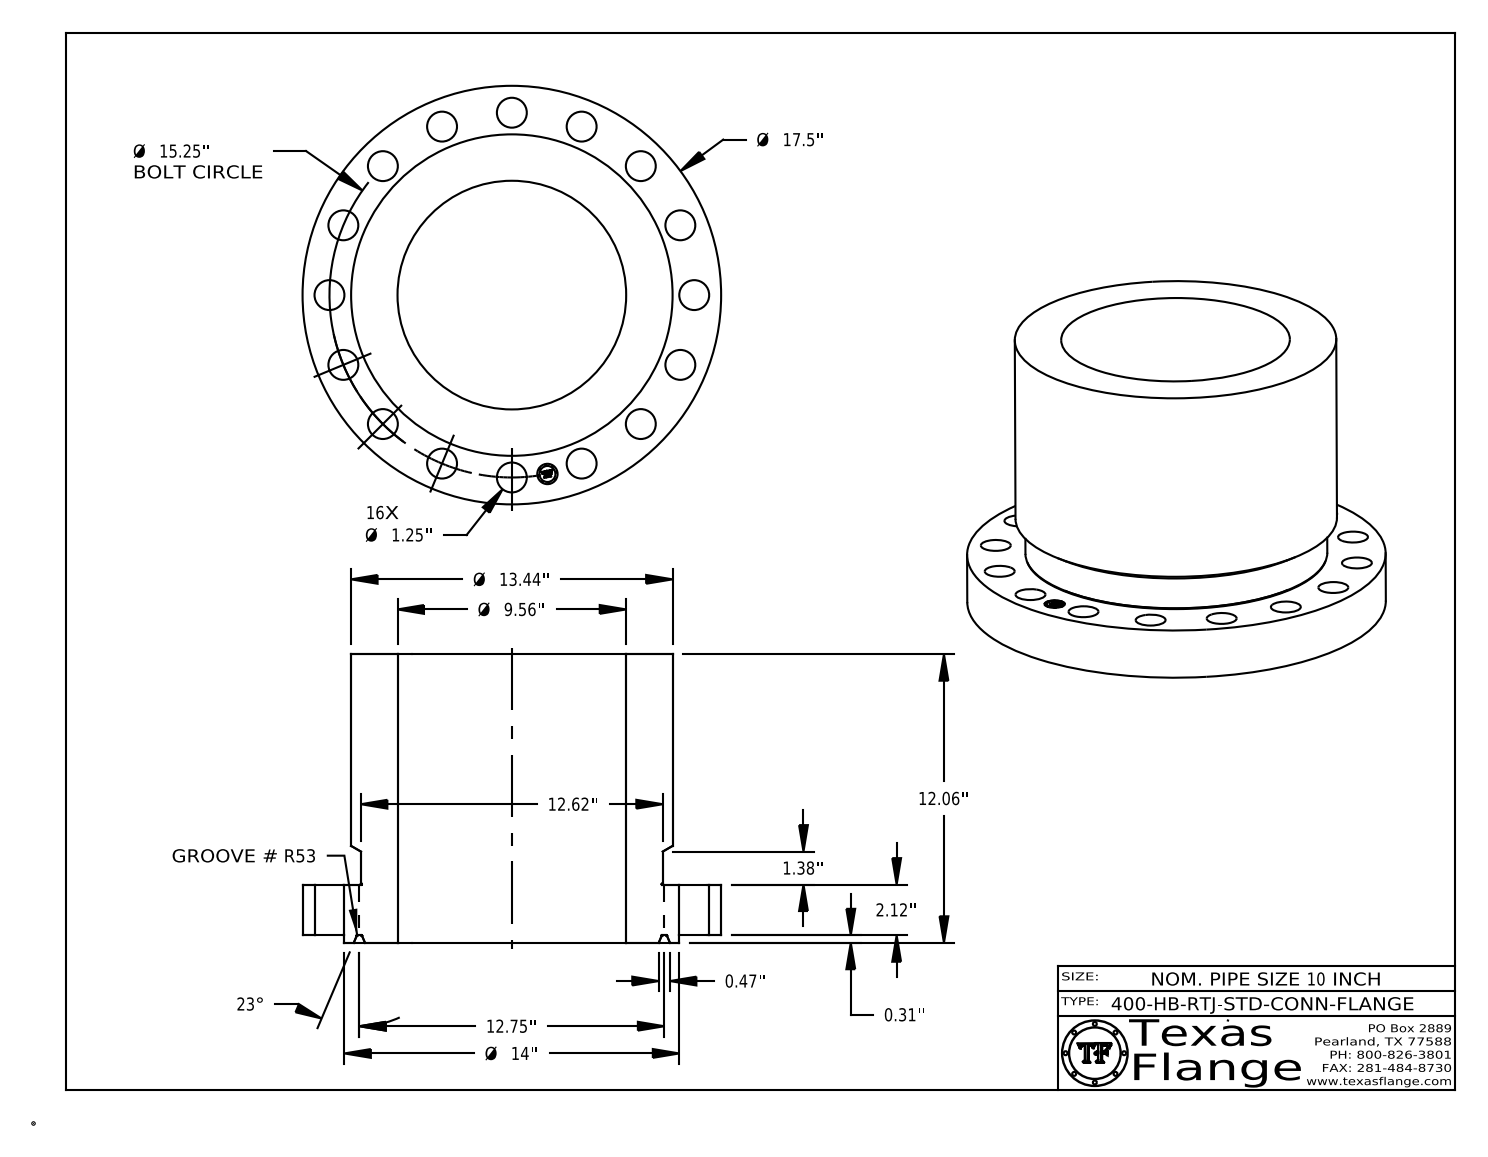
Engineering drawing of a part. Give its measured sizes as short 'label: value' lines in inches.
name: 10-400-HB-RTJ-STD-CONN-FLANGE
written by: CATIA V5 STEP AP214 (AUTOMOTIVE_DESIGN)
unit: in
bodies: 1 solid, 447 faces (371 planar, 62 cylindrical, 14 other)
size: 17.5 × 17.5 × 12.063
volume: 987.4 in³; area: 1 371 in²
holes: 16× ⌀1.25, 1× ⌀0.85, 1× ⌀9.56
bosses: 8× ⌀0.051, 1× ⌀17.5, 1× ⌀14, 1× ⌀13.44, 1× ⌀12.62, 1× ⌀0.67
face distances: 2.12, 11.75, 9.63, 0.313, 2.433, 12.063, 2.428, 2.115, 9.635, 0.254
hole spacings: 8.472, 10.783, 14.957, 14.089, 7.625, 2.975, 2.975, 5.836
